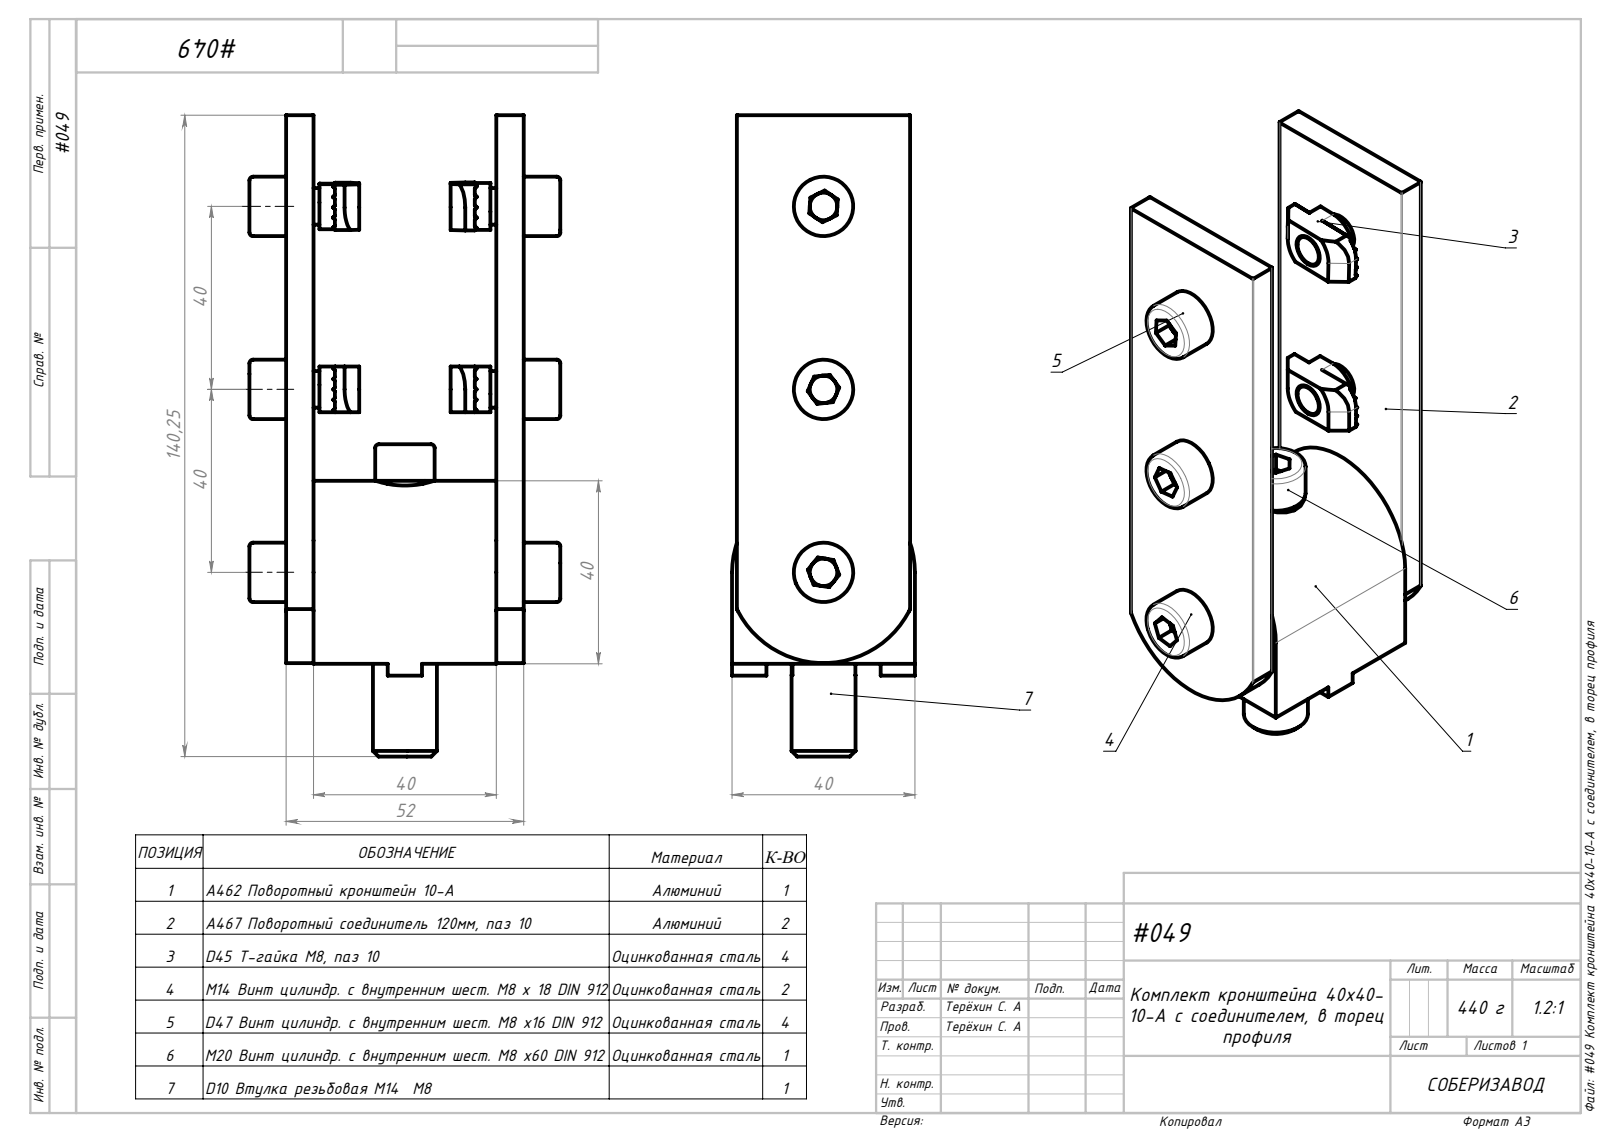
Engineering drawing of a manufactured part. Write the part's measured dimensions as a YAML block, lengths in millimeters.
part_name: "#049 Комплект кронштейна 40х40-10-А с соединителем, в торец профиля; A467 Поворотный соединитель 120мм, паз 10; D47 Винт цилиндр. с внутренним шест. М8 х16 DIN 912; M14 Винт цилиндр. с внутренним шест. М8 х 18 DIN 912 (+4 more)"
step_written_by: "SolidWorks 2021 (AUTOMOTIVE_DESIGN)"
units: millimeters
bodies: {solids: 15, faces: 479, planar: 290, cylindrical: 87, other: 102}
overall_size: [140.25, 68, 40]
volume: 124524
surface_area: 45186
round_holes:
  - {diameter: 8.5, count: 4}
  - {diameter: 6.7, count: 2}
  - {diameter: 6.5, count: 1}
  - {diameter: 7, count: 1}
  - {diameter: 12.7, count: 1}
round_bosses_or_shafts:
  - {diameter: 13, count: 4}
  - {diameter: 8, count: 4}
  - {diameter: 14, count: 1}
partial_cylinders:
  - {radius: 0.2, count: 8}
  - {radius: 6, count: 8}
  - {radius: 5.67, count: 4}
  - {radius: 20, count: 1}
  - {radius: 21.12, count: 1}
face_to_face_distances: [6, 46, 40, 52, 1.05, 38.95, 37.9, 10, 8, 16]
hole_center_spacings: [40, 80]
